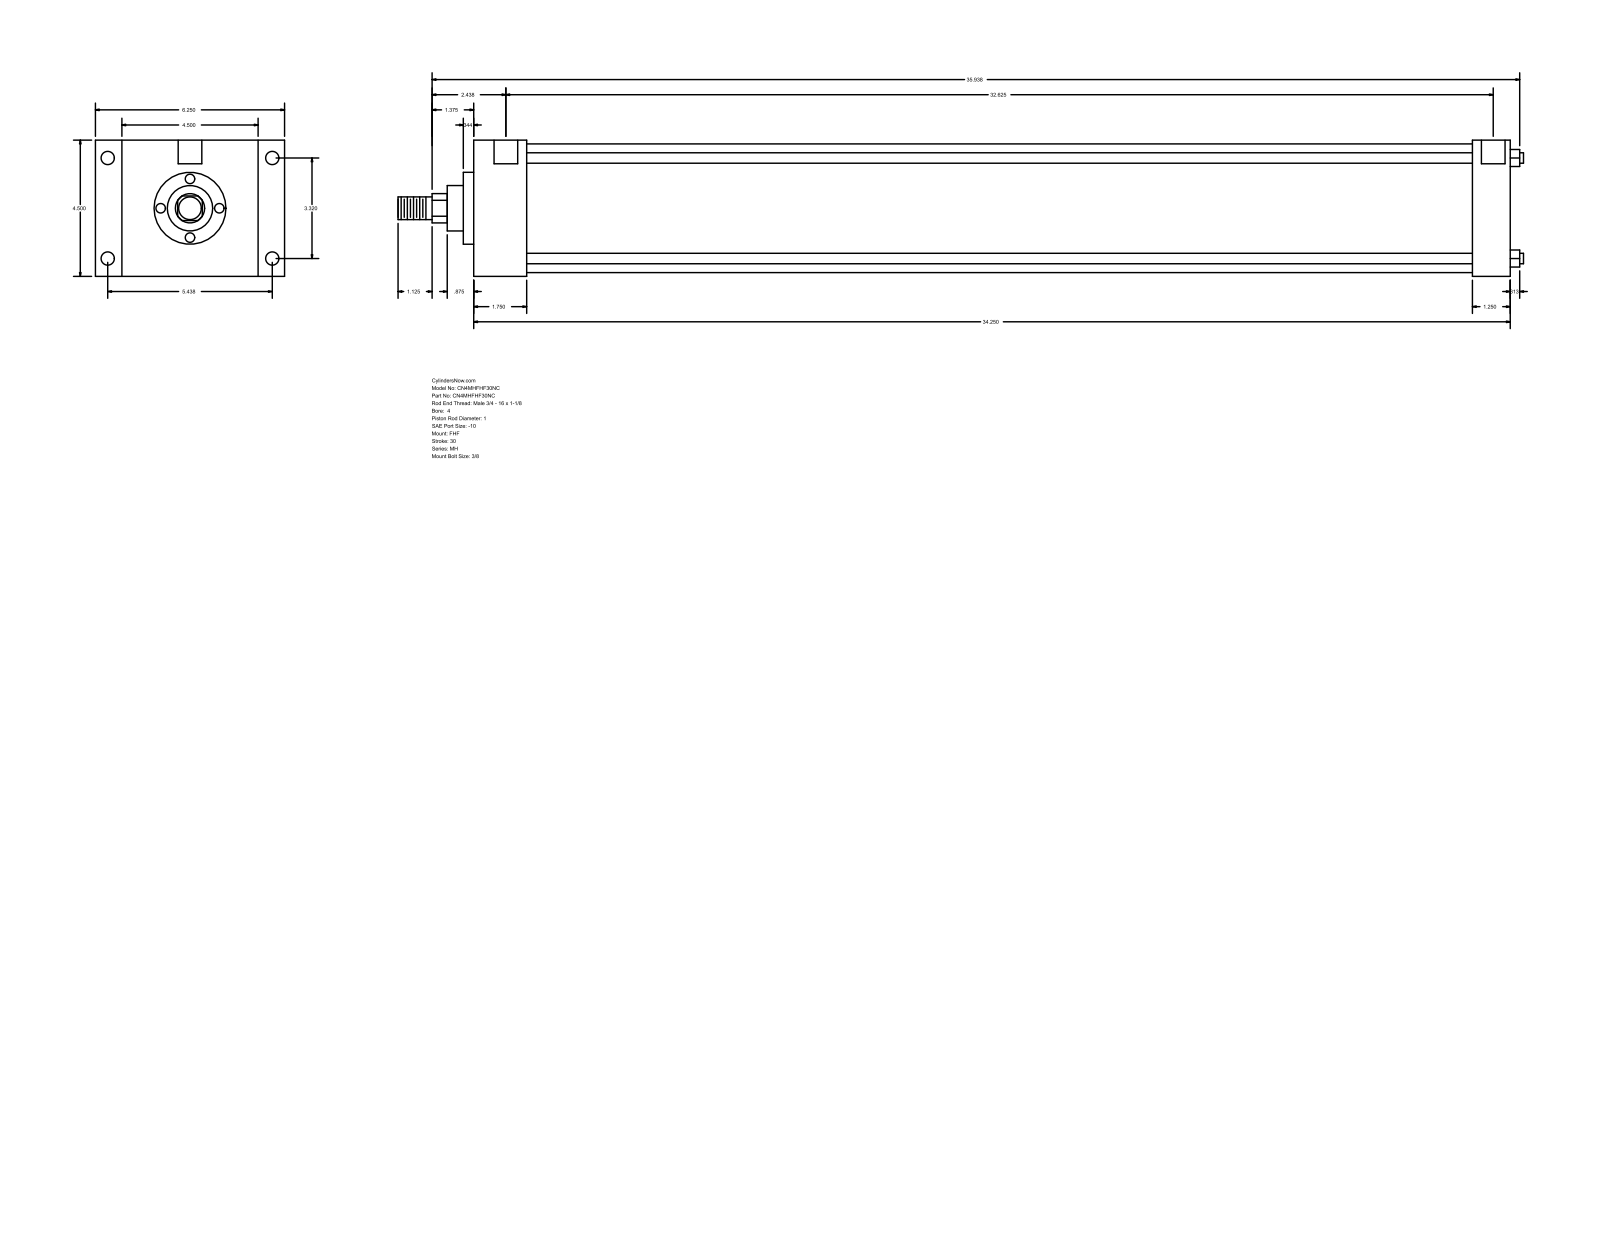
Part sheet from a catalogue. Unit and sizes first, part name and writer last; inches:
Units: inches
Overall size (bounding box): 37.187 × 6.25 × 4.5
Round holes (diameter × count): ⌀0.344 ×4, ⌀0.438 ×4, ⌀0.781 ×2
Round bosses / shafts (diameter × count): ⌀0.345 ×4, ⌀4.25 ×1, ⌀2.375 ×1, ⌀1.5 ×1, ⌀1 ×1, ⌀0.75 ×1
Partial cylindrical surfaces — rounded edges, fillets, slot ends (radius × count): R0.484 ×1
Main face-to-face distances: 4.5, 34.25, 1.75, 32.5, 0.875, 5.375, 6.25, 33, 31.25, 1.25
Hole centre spacings: 0.062, 3.32, 5.438, 6.371, 32.687, 32.75, 32.625
Bodies: 0 solids, 90 faces (61 planar, 29 cylindrical, 0 other)
Part name (STEP PRODUCT): MH_FHF__0400_1
STEP written by: GSSL Pune (CONFIG_CONTROL_DESIGN)
